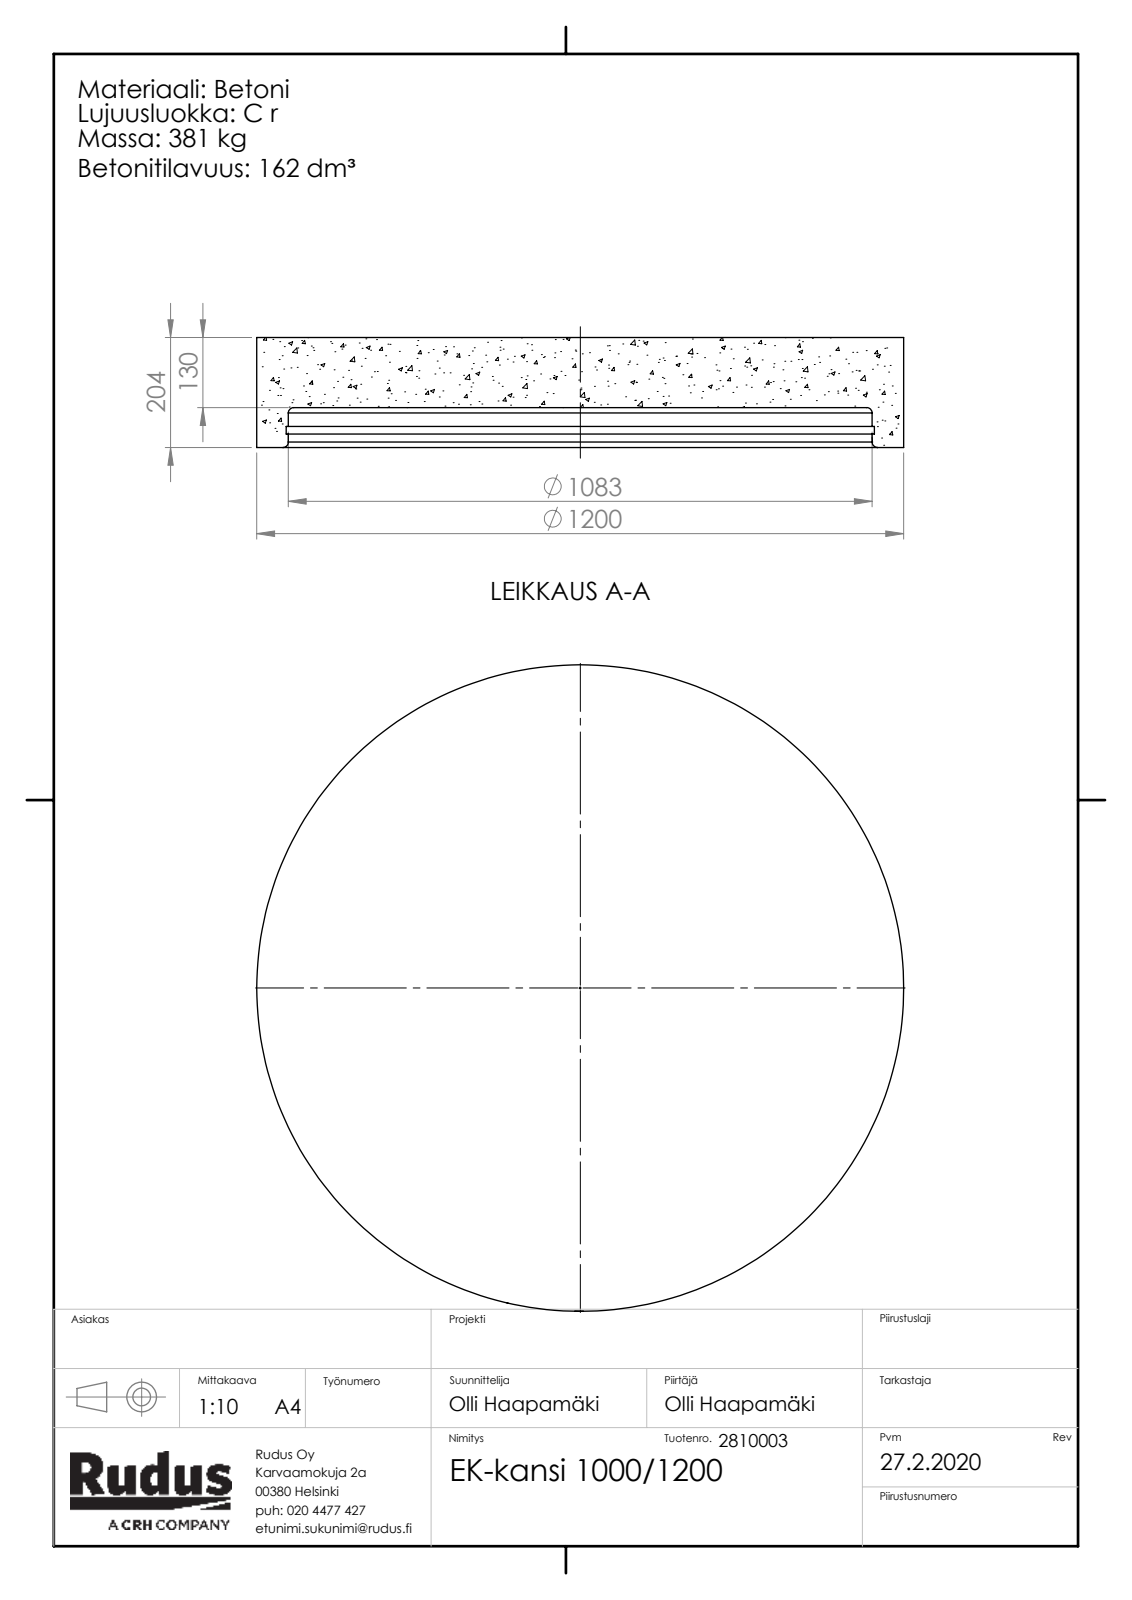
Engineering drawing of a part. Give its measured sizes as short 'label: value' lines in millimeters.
name: Rudus 2810003 EK-kansi 1000_1200; EK-osa-kansi_Umpi
written by: SolidWorks 2019 (CONFIG_CONTROL_DESIGN)
unit: mm
bodies: 1 solid, 94 faces (5 planar, 15 cylindrical, 74 other)
size: 1200 × 1200 × 204
volume: 162 300 000 mm³; area: 3 286 000 mm²
holes: 1× ⌀1083, 1× ⌀1091
bosses: 1× ⌀1200
rounds: 1× R597
face distances: 130, 74, 204, 25, 39, 14, 49, 179, 35, 165
